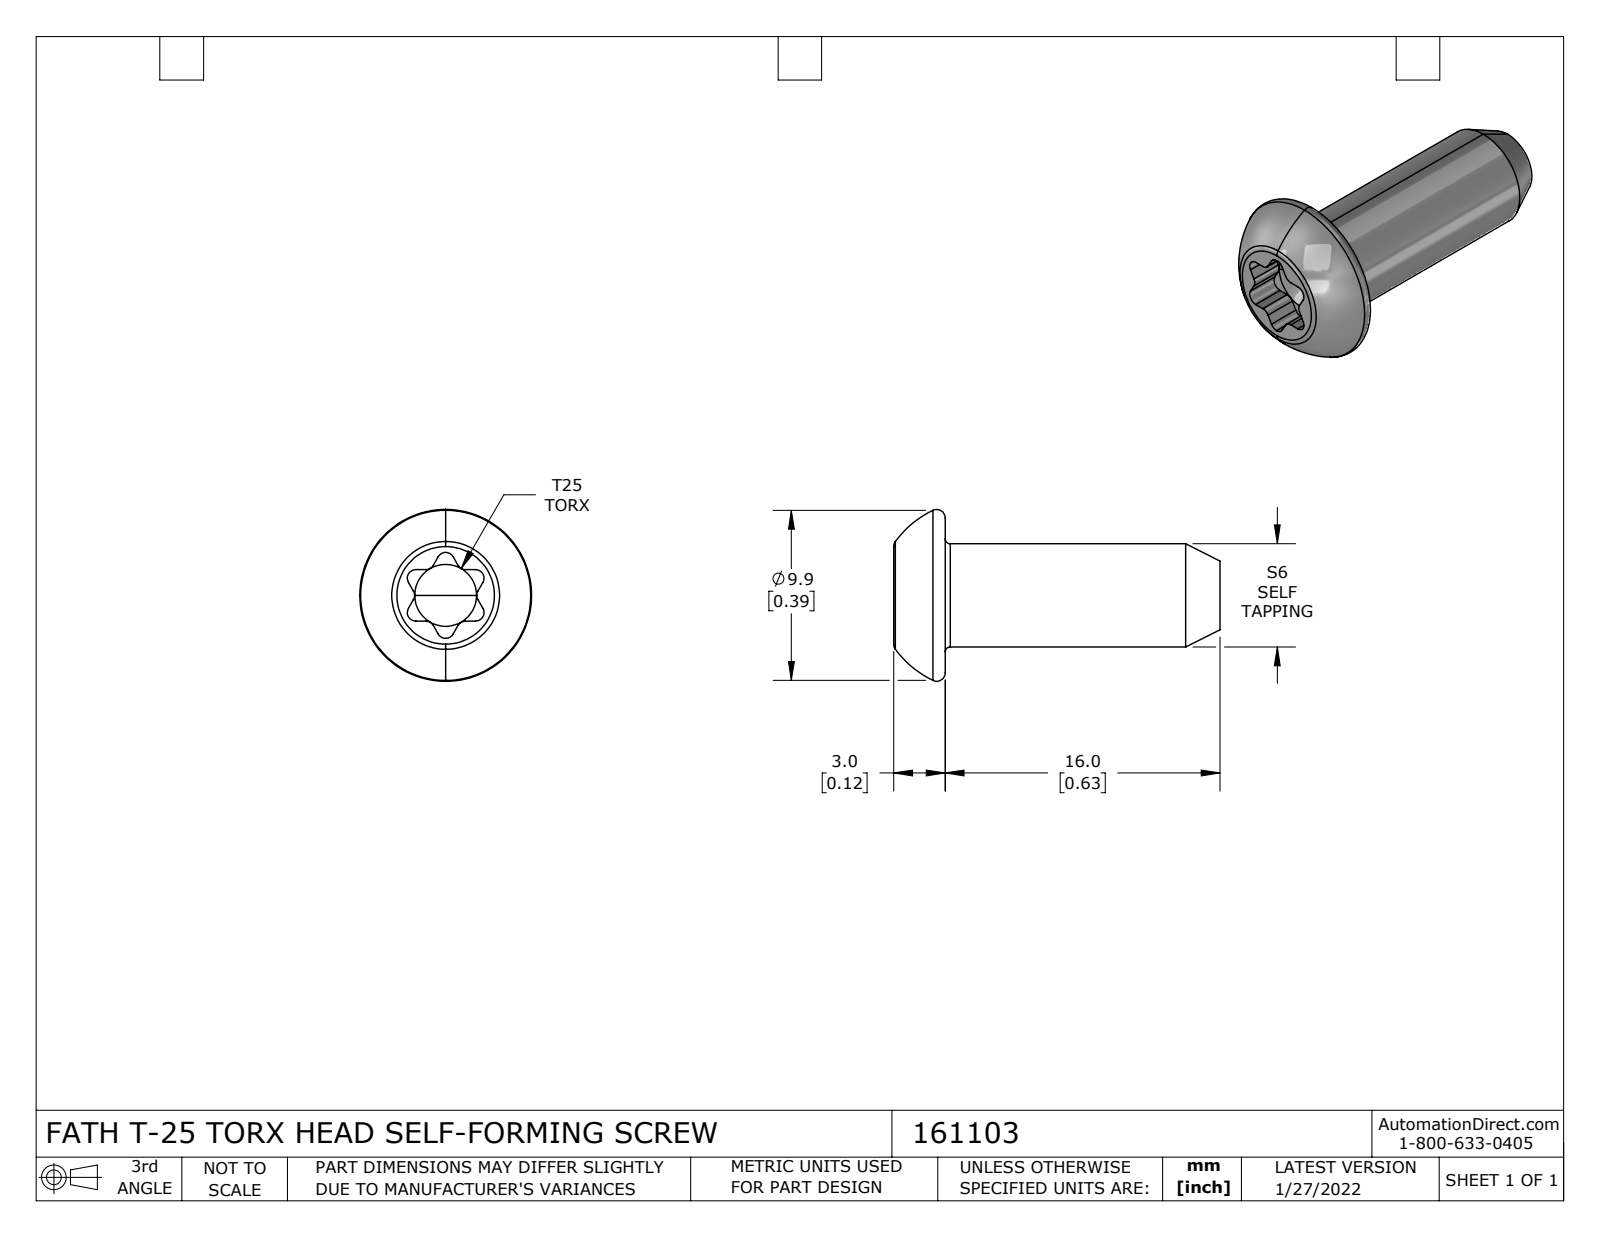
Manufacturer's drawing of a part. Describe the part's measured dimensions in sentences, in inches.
The part is named "161103". Its 3-D file was written by "SolidWorks 2021 (CONFIG_CONTROL_DESIGN)". It is 1 solid with 43 faces: 16 planar, 15 cylindrical and 12 other. Overall it measures 0.748 by 0.394 by 0.394 inches. Its volume is 0.036 cubic inches and its surface area 0.798 square inches. Round bosses or shafts: 1 of diameter 0.236. Partial cylindrical surfaces (rounded edges, fillets, slot ends): 12 of radius 0.02. The main face-to-face distances are 0.118, 0.63, 0.748, 0.669, 0.039, 0.079.
